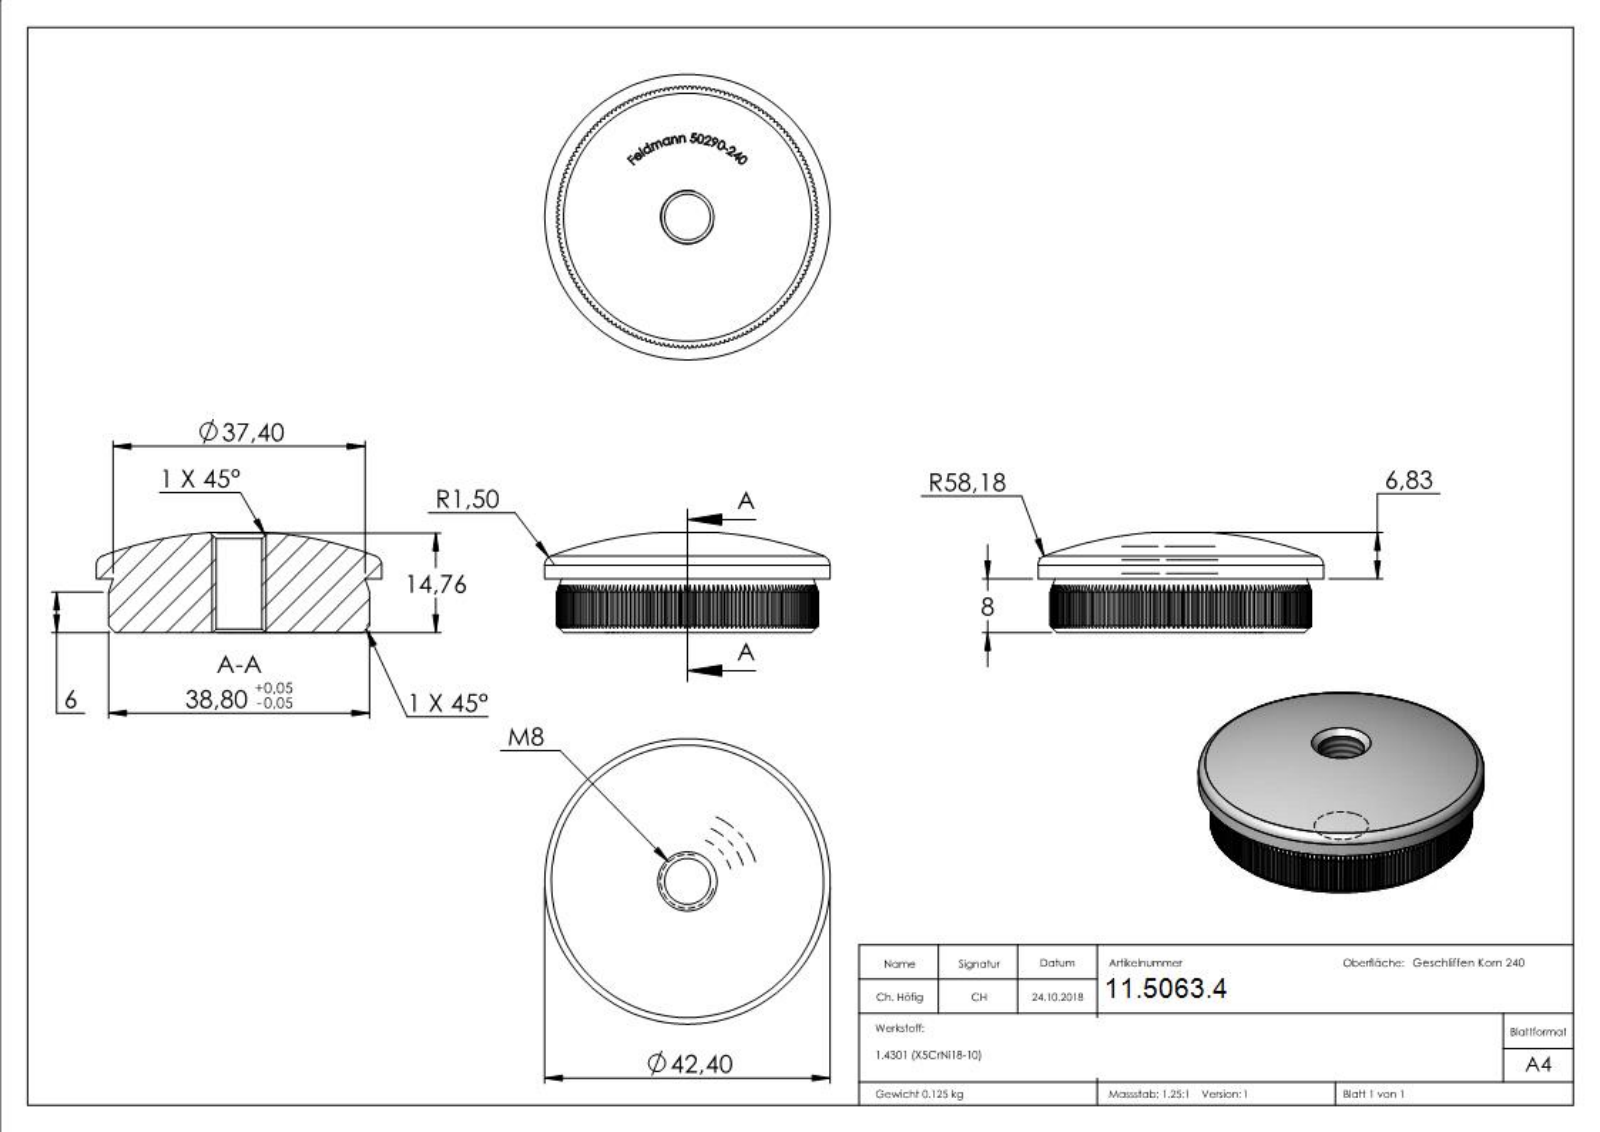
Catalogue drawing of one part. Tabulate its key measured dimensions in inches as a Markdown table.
| quantity | value |
| --- | --- |
| part name | 50290-240 |
| STEP written by | SolidWorks 2015 (CONFIG_CONTROL_DESIGN) |
| units | inches |
| bodies | 1 solid, 753 faces (472 planar, 174 cylindrical, 107 other) |
| overall size | 1.669 × 1.669 × 0.584 |
| volume | 0.962 in³ |
| surface area | 7.524 in² |
| round holes (diameter × count) | 0.268 × 1 |
| round bosses / shafts (diameter × count) | 1.669 × 1 |
| partial cylindrical surfaces (radius × count) | 0.764 × 1 |
| main face-to-face distances | 0.315, 0.75, 0.75, 0.751, 0.311, 0.749, 0.026, 0.021, 0.026, 0.031 |
